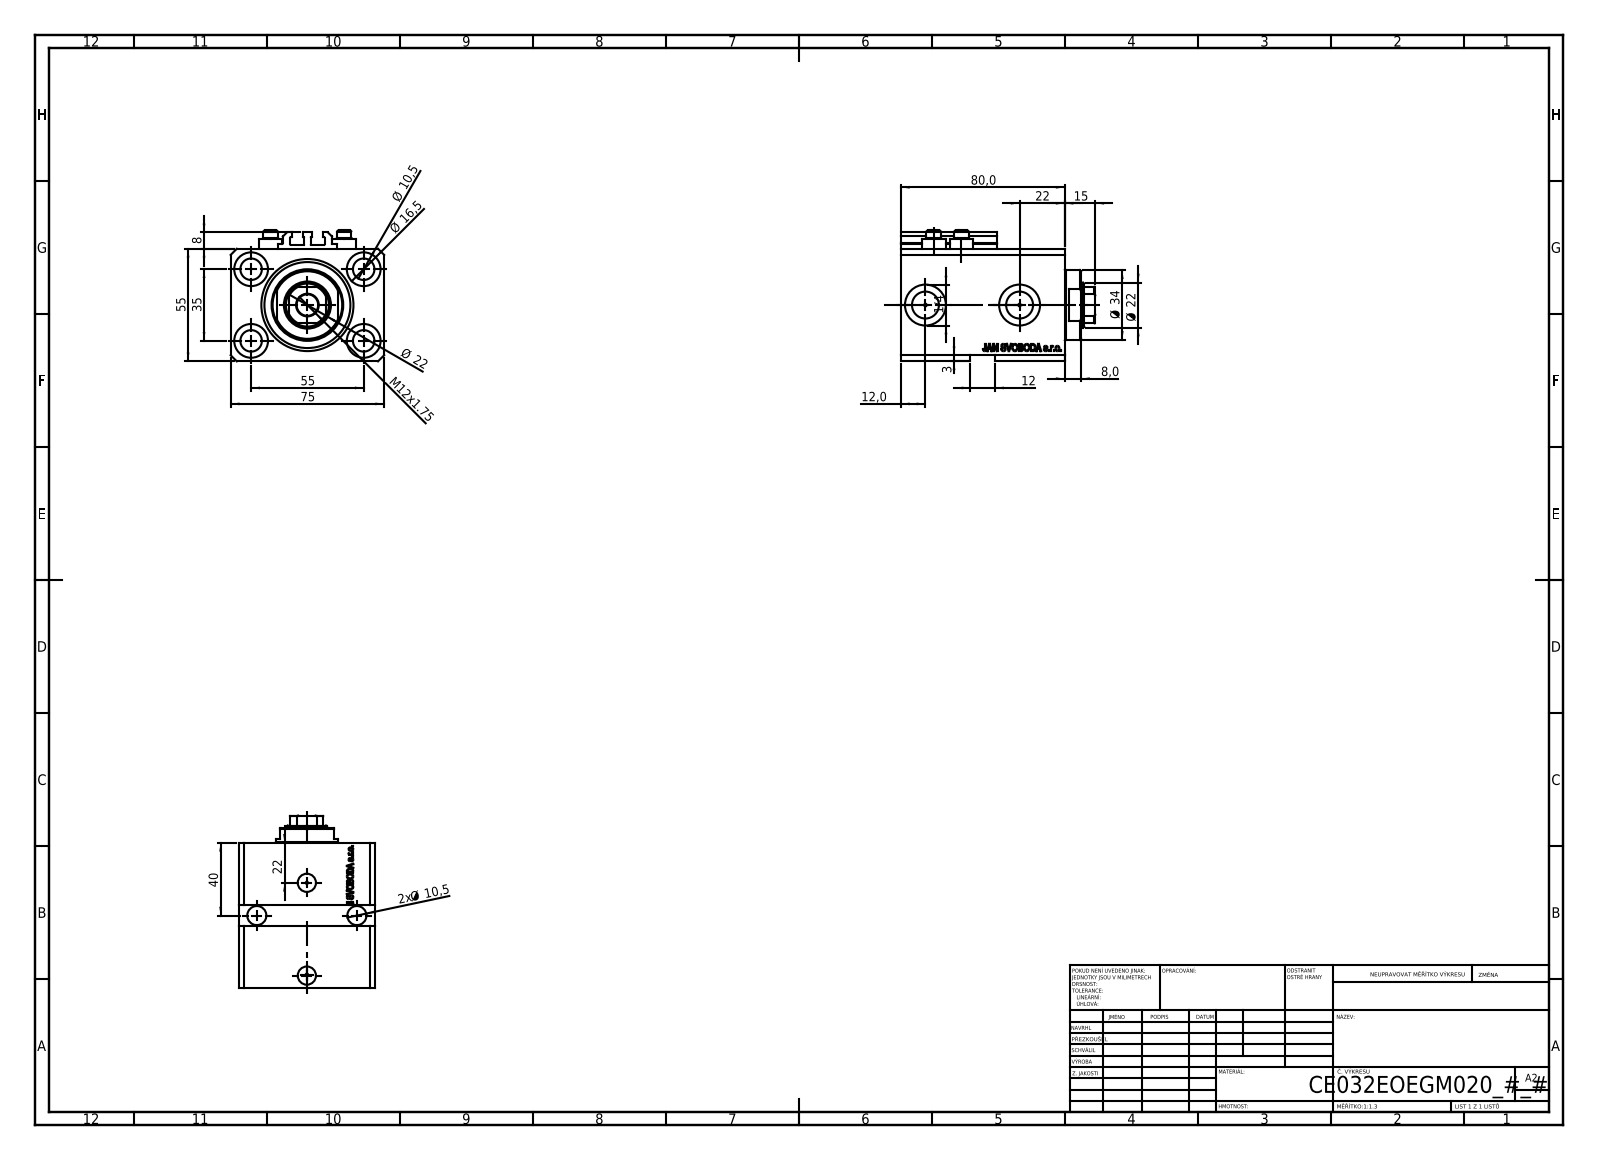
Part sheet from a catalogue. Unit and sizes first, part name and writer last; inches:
Units: inches
Overall size (bounding box): 3.74 × 2.953 × 2.52
Round holes (diameter × count): ⌀0.413 ×7, ⌀0.049 ×4, ⌀0.157 ×4, ⌀0.65 ×4, ⌀0.394 ×2, ⌀0.518 ×2, ⌀0.787 ×2, ⌀0.866 ×1, ⌀1.26 ×1, ⌀1.772 ×1
Round bosses / shafts (diameter × count): ⌀0.457 ×4, ⌀0.276 ×4, ⌀1.339 ×1
Partial cylindrical surfaces — rounded edges, fillets, slot ends (radius × count): R0.008 ×10, R0.413 ×1
Main face-to-face distances: 2.165, 2.953, 0.591, 3.15, 2.559, 0.118, 2.169, 0.39, 2.76, 2.126
Hole centre spacings: 1.283, 2.165, 0.535, 0.555, 0.783, 0.792, 1.016, 1.121
Volume: 17.32 in³ · Surface area: 115.4 in²
Bodies: 8 solids, 1064 faces (514 planar, 126 cylindrical, 424 other)
Part name (STEP PRODUCT): V250CE_E_Body; V250CE_VC_E; ALLEN BOLT V250CE; V250CE_C_VCP
STEP written by: SolidWorks 2019 (CONFIG_CONTROL_DESIGN)
